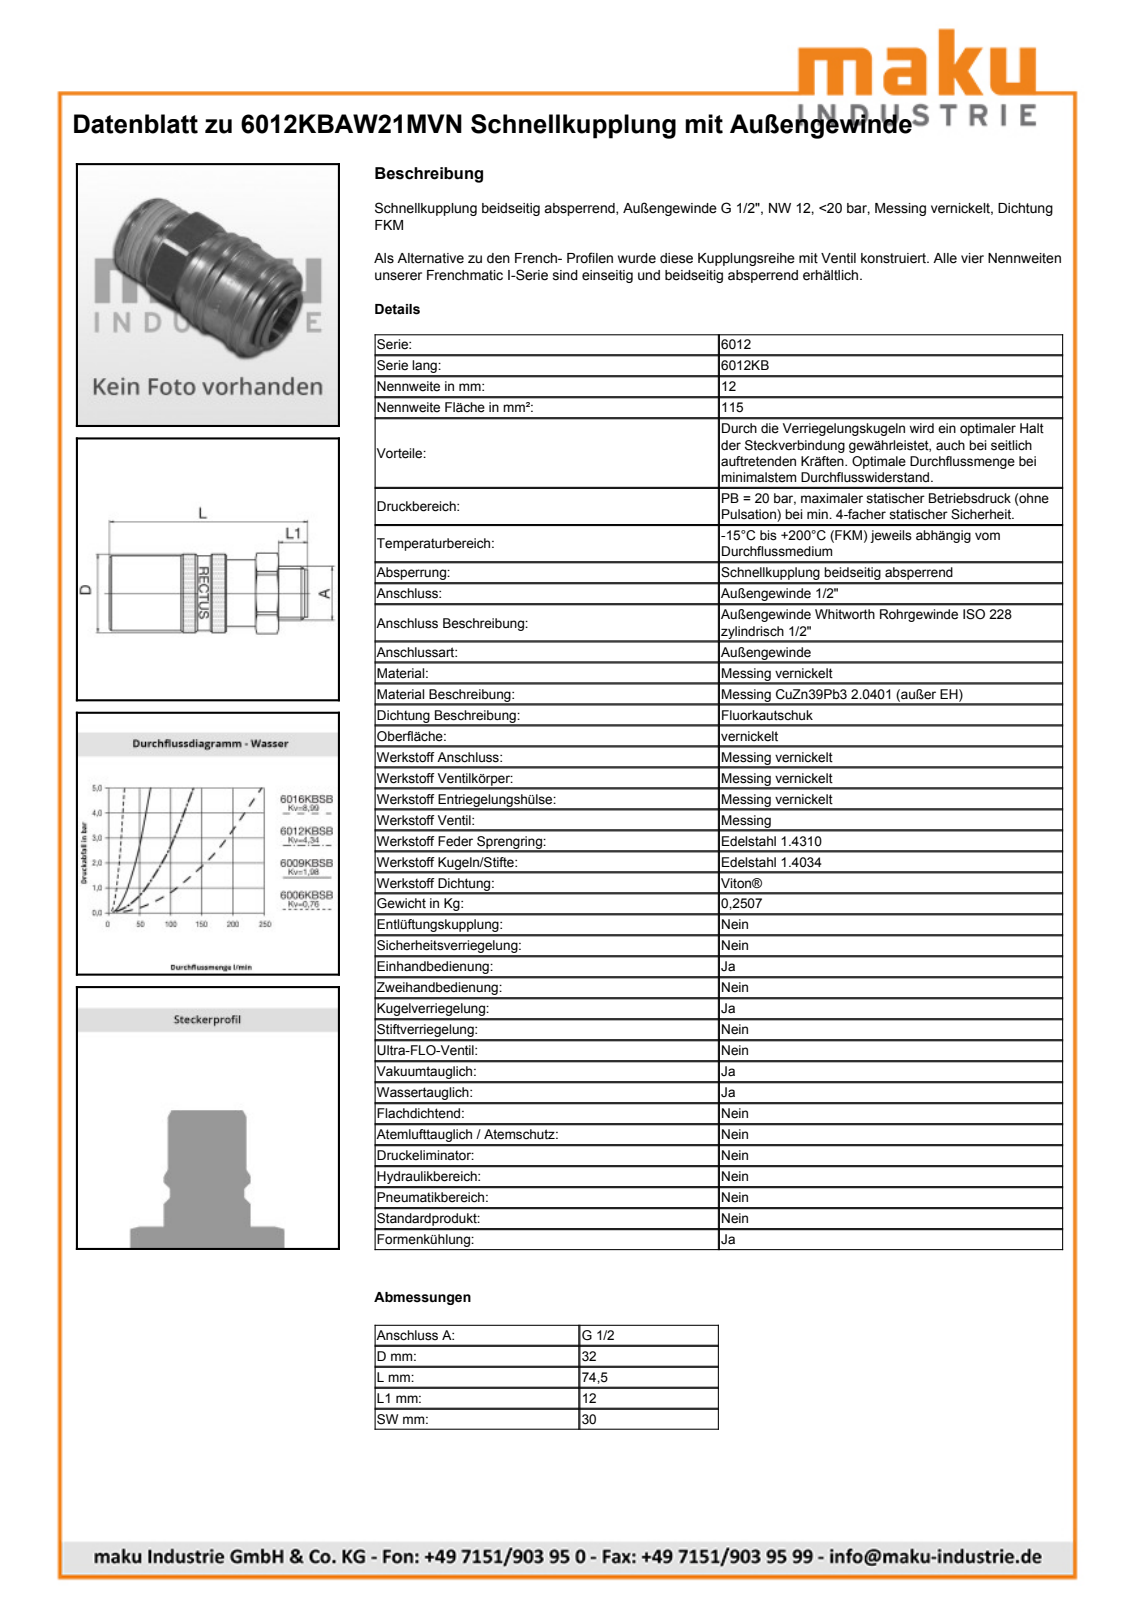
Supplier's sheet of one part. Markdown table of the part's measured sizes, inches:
| quantity | value |
| --- | --- |
| part name | D107315 |
| STEP written by | Autodesk Inventor 2013 (AUTOMOTIVE_DESIGN) |
| units | inches |
| bodies | 3 solids, 638 faces (199 planar, 76 cylindrical, 363 other) |
| overall size | 2.933 × 1.332 × 1.26 |
| volume | 2.913 in³ |
| surface area | 26.91 in² |
| round holes (diameter × count) | 0.953 × 1, 1.024 × 1, 1.039 × 1, 1.154 × 1 |
| round bosses / shafts (diameter × count) | 1.26 × 1, 1.22 × 1, 1.213 × 1, 1.142 × 1, 1.102 × 1, 0.984 × 1, 0.945 × 1, 0.886 × 1 |
| partial cylindrical surfaces (radius × count) | 0.424 × 1, 0.667 × 1 |
| main face-to-face distances | 1.181, 2.461, 0.472, 2.402, 2.933, 0.512, 1.929, 0.531, 0.413, 1.988 |
